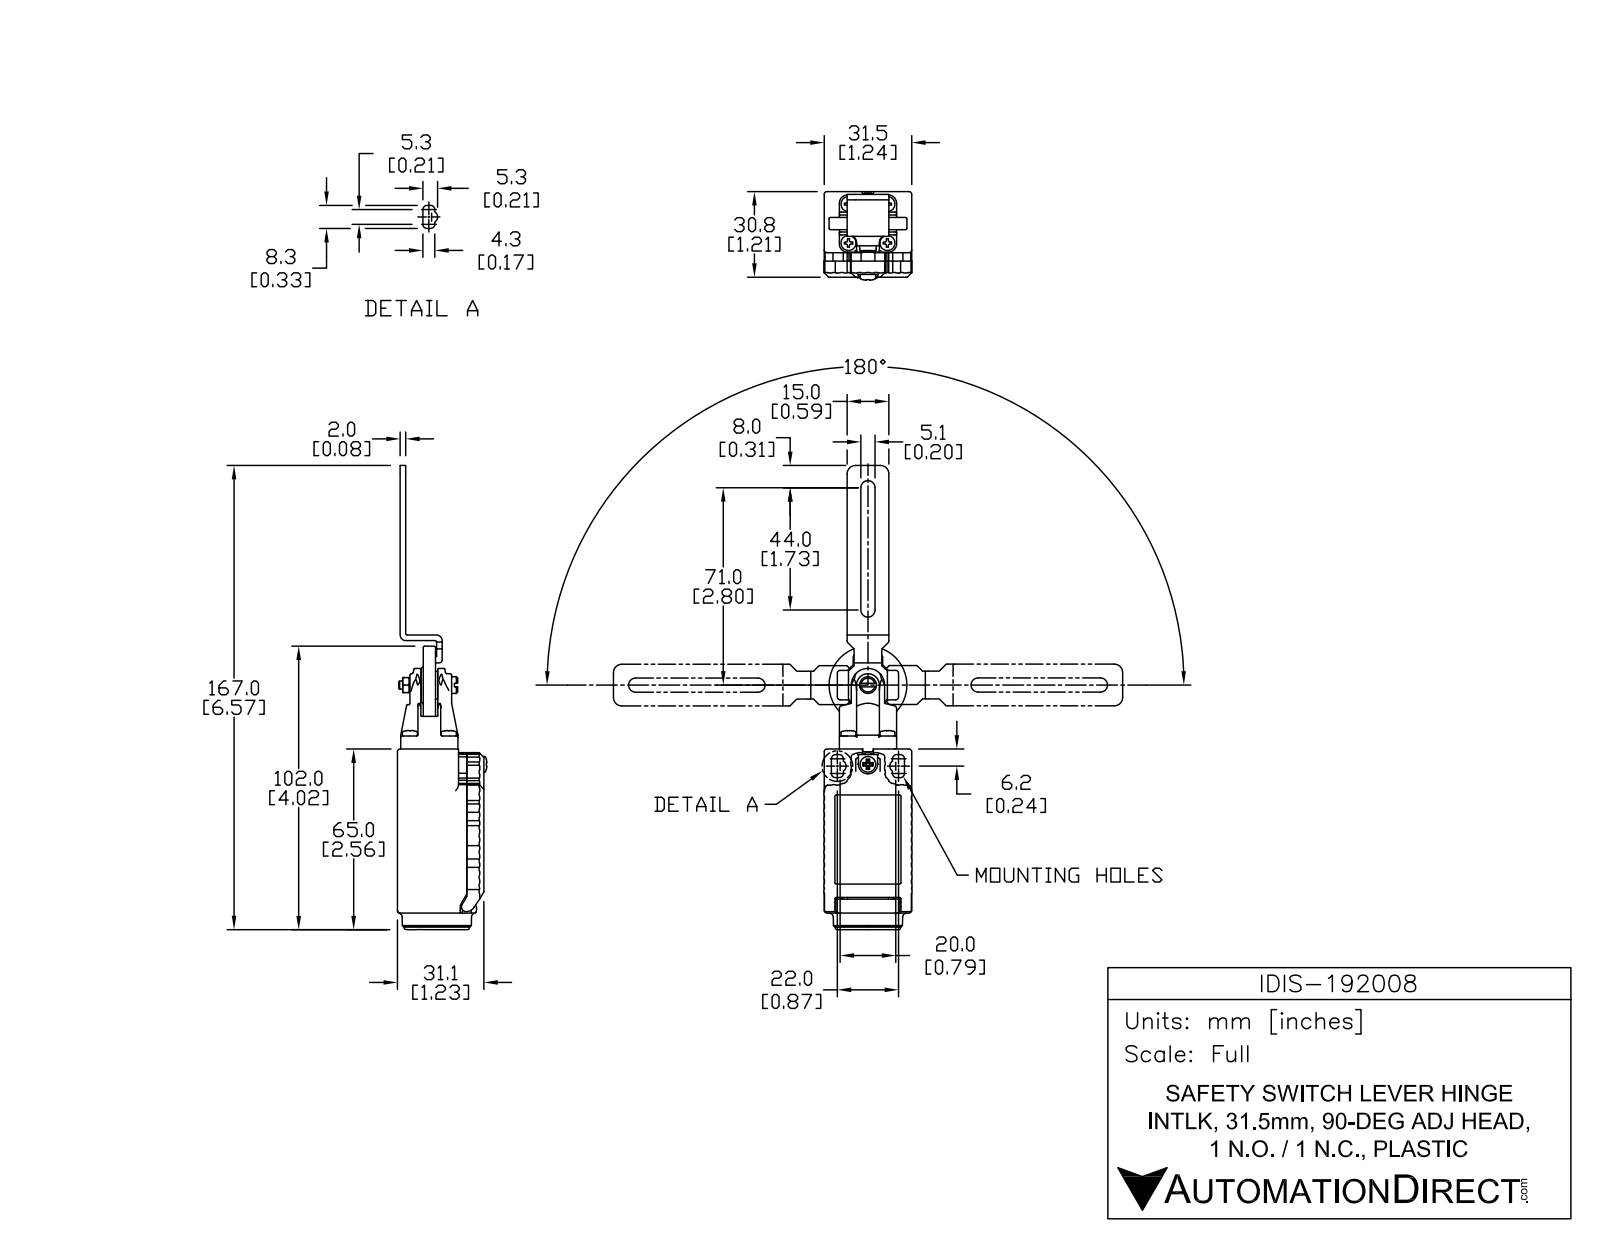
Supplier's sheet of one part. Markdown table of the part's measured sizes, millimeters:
| quantity | value |
| --- | --- |
| part name | IDIS-192008 |
| STEP written by | SolidWorks 2013 (AUTOMOTIVE_DESIGN) |
| units | millimeters |
| bodies | 1 solid, 668 faces (270 planar, 240 cylindrical, 158 other) |
| overall size | 176.7 × 32.2 × 31.5 |
| volume | 67 552 mm³ |
| surface area | 21 014 mm² |
| round holes (diameter × count) | 4 × 2, 3 × 1, 16.19 × 1, 18.5 × 1, 21.2 × 1 |
| round bosses / shafts (diameter × count) | 5.4 × 4, 28 × 1, 25 × 1, 23 × 1, 17.19 × 1, 13.4 × 1, 10 × 1, 6 × 1 |
| partial cylindrical surfaces (radius × count) | 0.5 × 71, 0.25 × 32, 1 × 11, 0.12 × 9, 1.5 × 8, 2.4 × 6, 3 × 6, 2 × 4 |
| main face-to-face distances | 31.5, 5.6, 0.5, 9.3, 1.9, 3.2, 2.8, 30.2, 20.9, 19 |
| hole center spacings | 22, 88.58, 88.59 |
